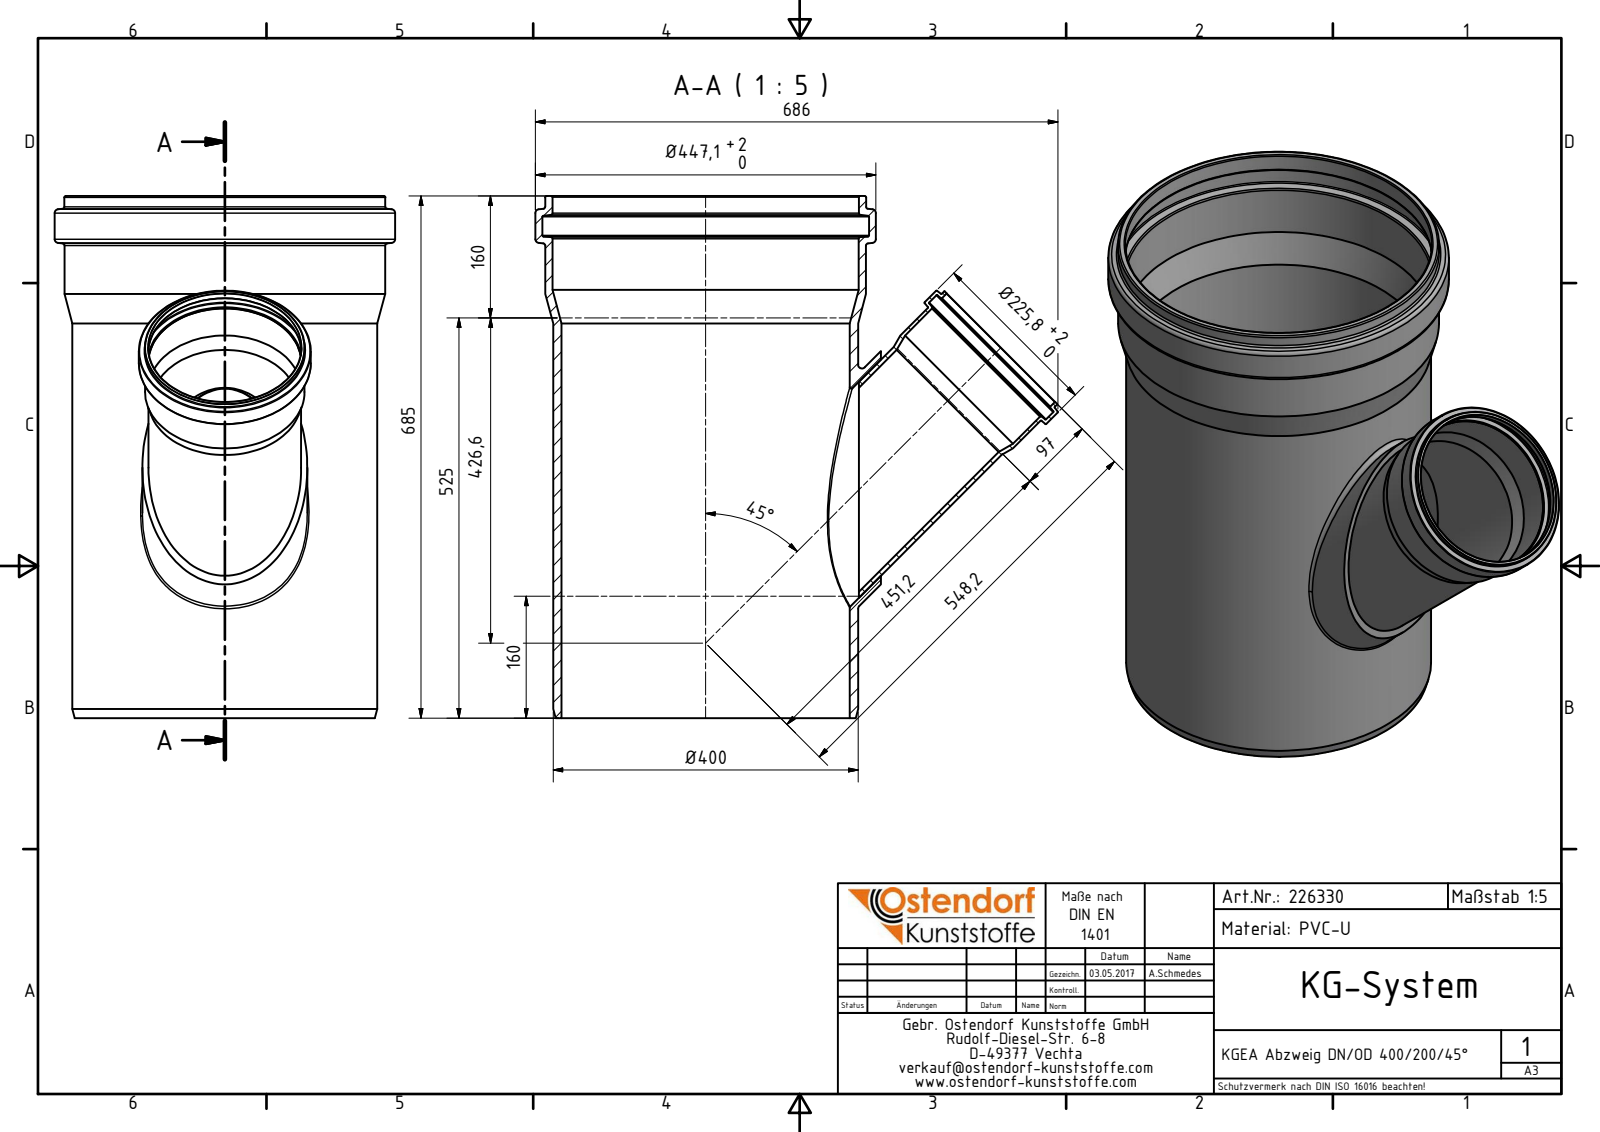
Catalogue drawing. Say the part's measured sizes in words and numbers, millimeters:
The part is named "226330 KGEA Abzweig DN_OD 400_200_45°; 226330 KGEA Abzweig DN_OD 400_200_45° Abzweig". Its 3-D file was written by "Autodesk Inventor 2016 (AUTOMOTIVE_DESIGN)". It is 2 solids with 60 faces: 6 planar, 19 cylindrical and 35 other. Overall it measures 686 by 685 by 447.1 millimeters. Its volume is 10 070 000 cubic millimeters and its surface area 2 133 000 square millimeters. Round holes: 2 of diameter 200.9, 1 of diameter 189.3, 1 of diameter 200.5, 1 of diameter 200.6, 1 of diameter 217, 1 of diameter 378.35, 1 of diameter 402, 1 of diameter 402.4, 1 of diameter 429.1. Round bosses or shafts: 1 of diameter 447.1, 1 of diameter 421.4, 1 of diameter 421.1, 1 of diameter 400.35, 1 of diameter 225.8, 1 of diameter 216.5, 1 of diameter 209.7, 1 of diameter 209.4. The main face-to-face distances are 685, 29.06, 27.57.
